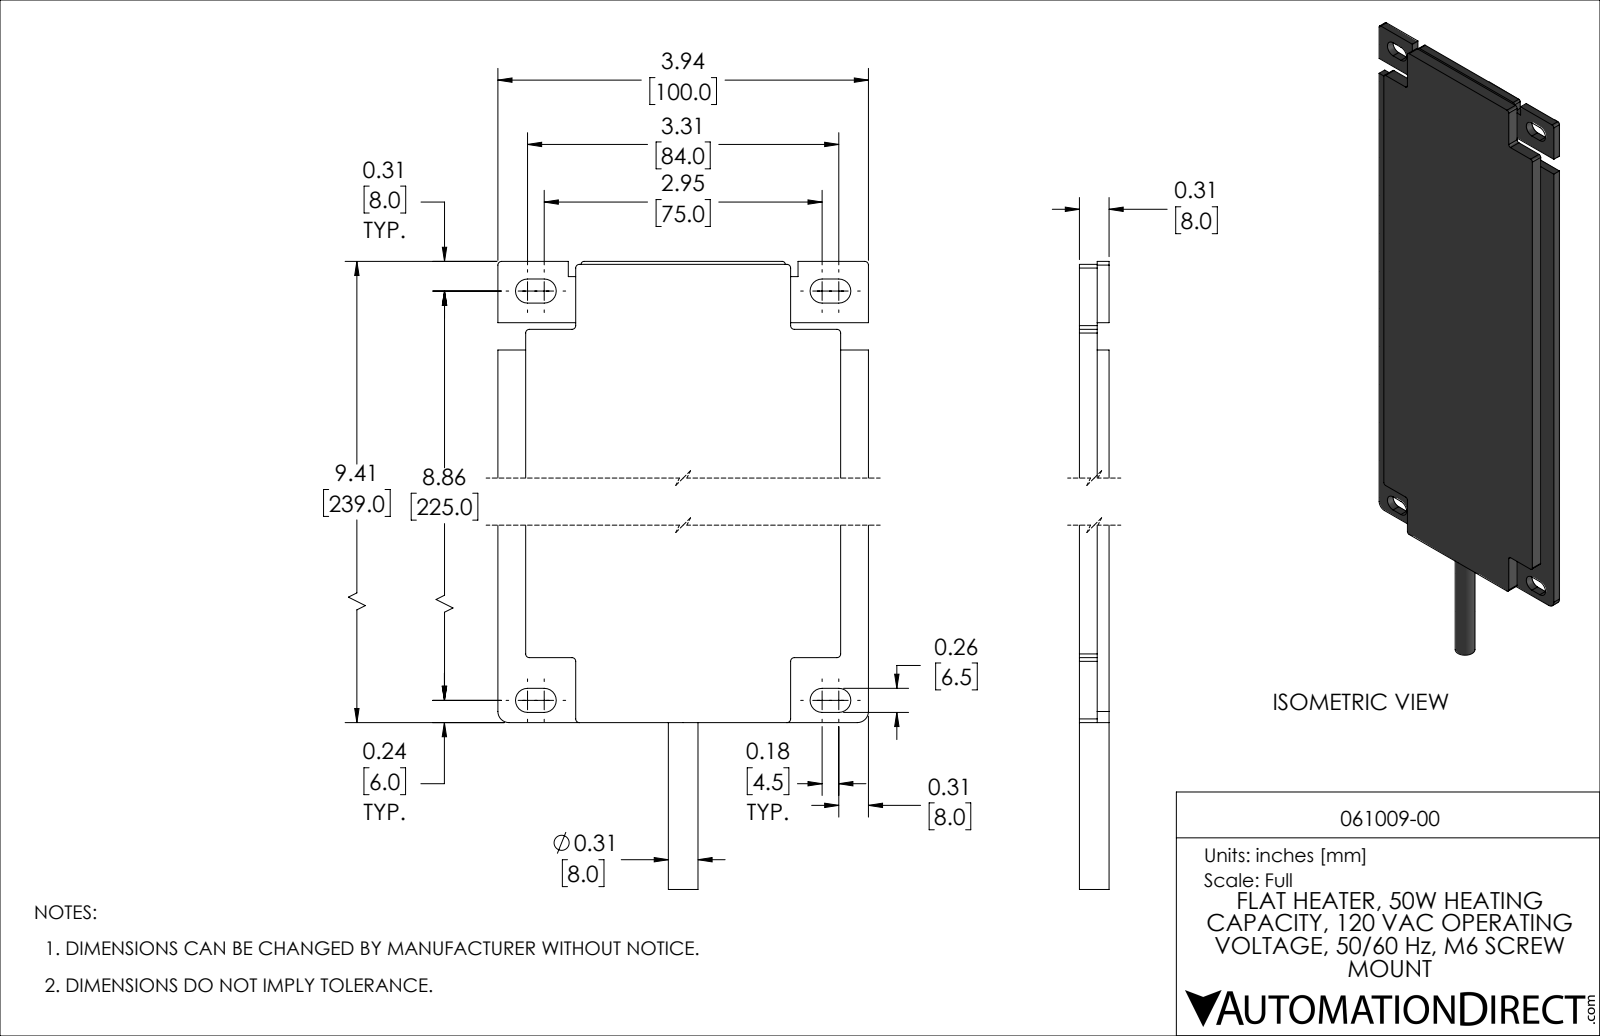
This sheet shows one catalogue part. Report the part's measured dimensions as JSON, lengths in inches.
{"part_name": "061009-00", "step_written_by": "SolidWorks 2019 (AUTOMOTIVE_DESIGN)", "units": "inches", "bodies": {"solids": 1, "faces": 75, "planar": 48, "cylindrical": 27, "other": 0}, "overall_size": [11.181, 3.937, 0.315], "volume_in3": 10.26, "surface_area_in2": 84.2, "round_bosses_or_shafts": [[0.315, 1]], "partial_cylinders_radius": [[0.039, 14], [0.128, 8], [0.031, 2], [0.118, 2]], "face_to_face_distances": [0.315, 0.189, 0.126, 0.295, 3.642, 3.346, 3.937, 8.469, 8.759, 0.29]}
